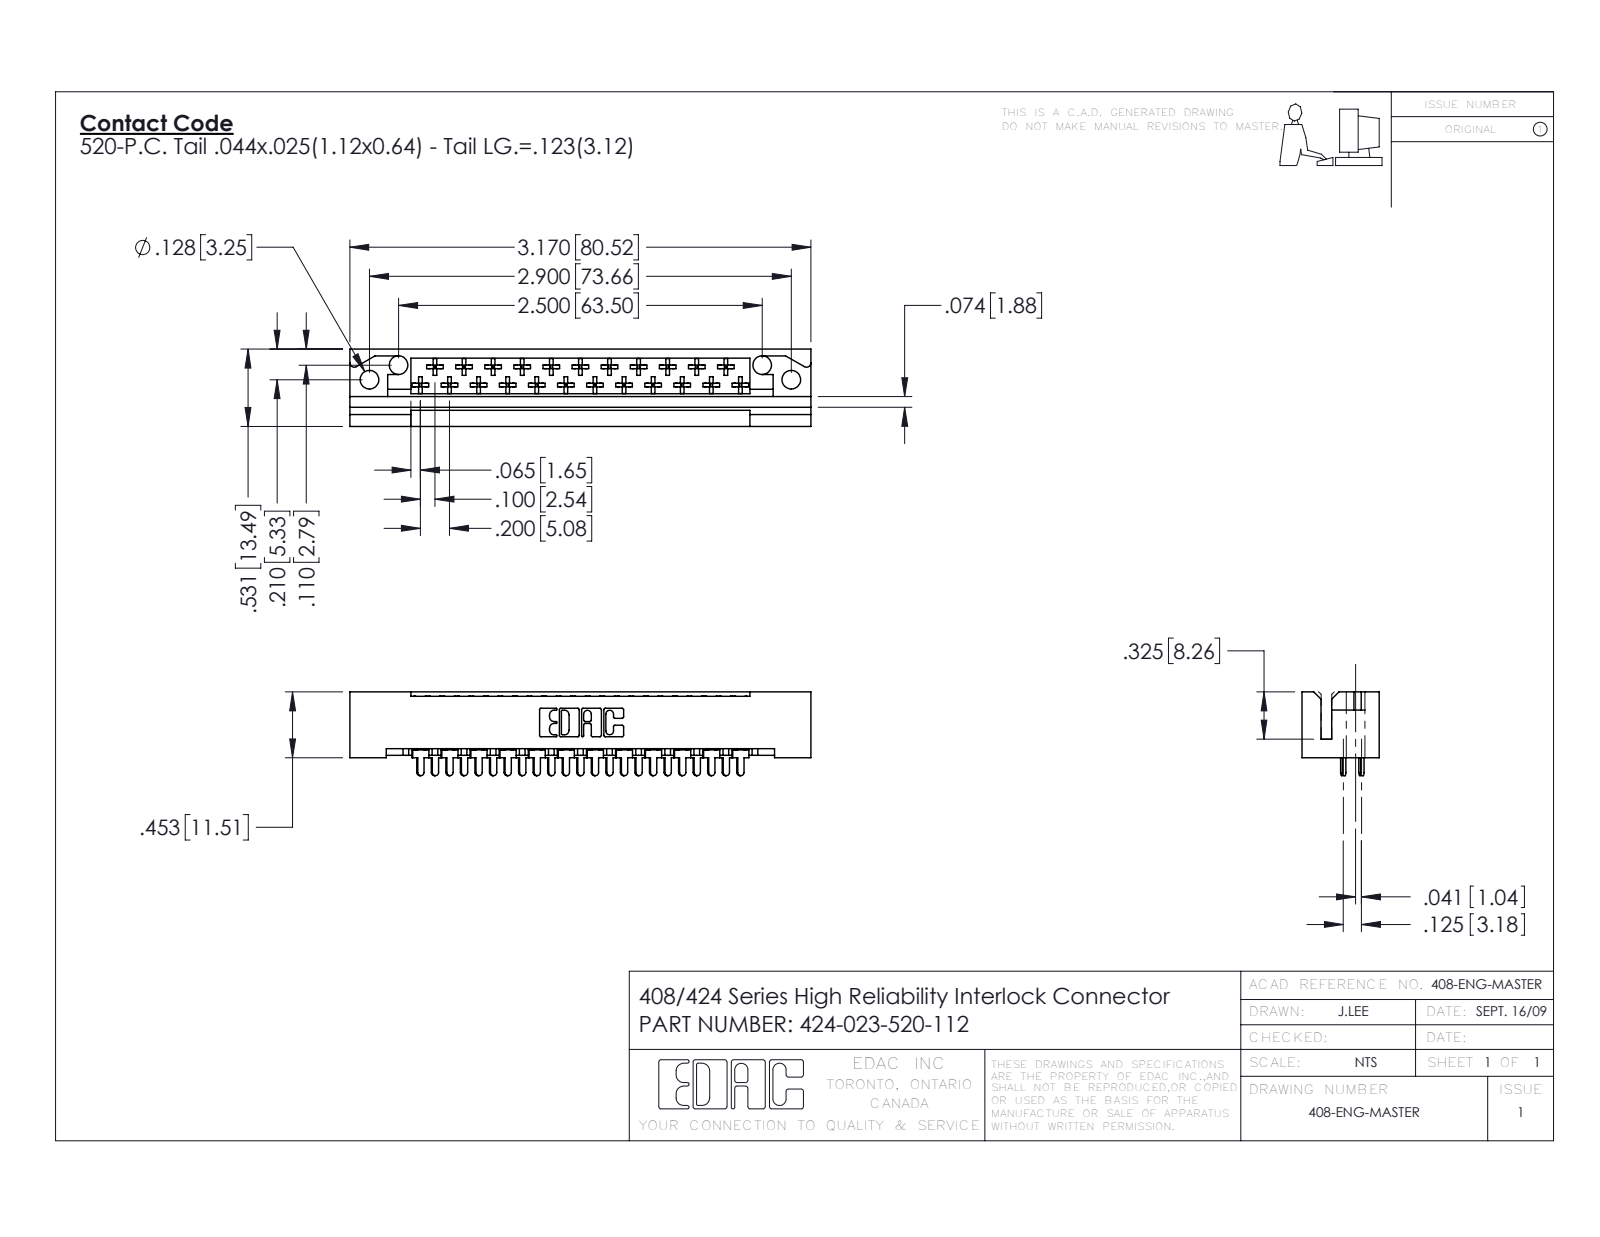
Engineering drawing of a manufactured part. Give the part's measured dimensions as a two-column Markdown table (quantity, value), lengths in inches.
| quantity | value |
| --- | --- |
| part name | 408-290-001_408-290-120; 424 Part_023; 424-023-520-112 |
| STEP written by | SolidWorks 2016 (CONFIG_CONTROL_DESIGN) |
| units | inches |
| bodies | 24 solids, 1410 faces (1055 planar, 263 cylindrical, 92 other) |
| overall size | 3.17 × 0.576 × 0.531 |
| volume | 0.534 in³ |
| surface area | 16.3 in² |
| round holes (diameter × count) | 0.128 × 4 |
| partial cylindrical surfaces (radius × count) | 0.01 × 138, 0.02 × 25, 0.022 × 23, 0.01 × 22, 0.007 × 6, 0.031 × 6, 0.026 × 3, 0.03 × 2 |
| main face-to-face distances | 0.4, 0.025, 0.531, 0.125, 0.1, 0.131, 0.326, 0.074, 0.205, 0.091 |
| hole center spacings | 0.224, 2.702, 2.5, 2.9 |
